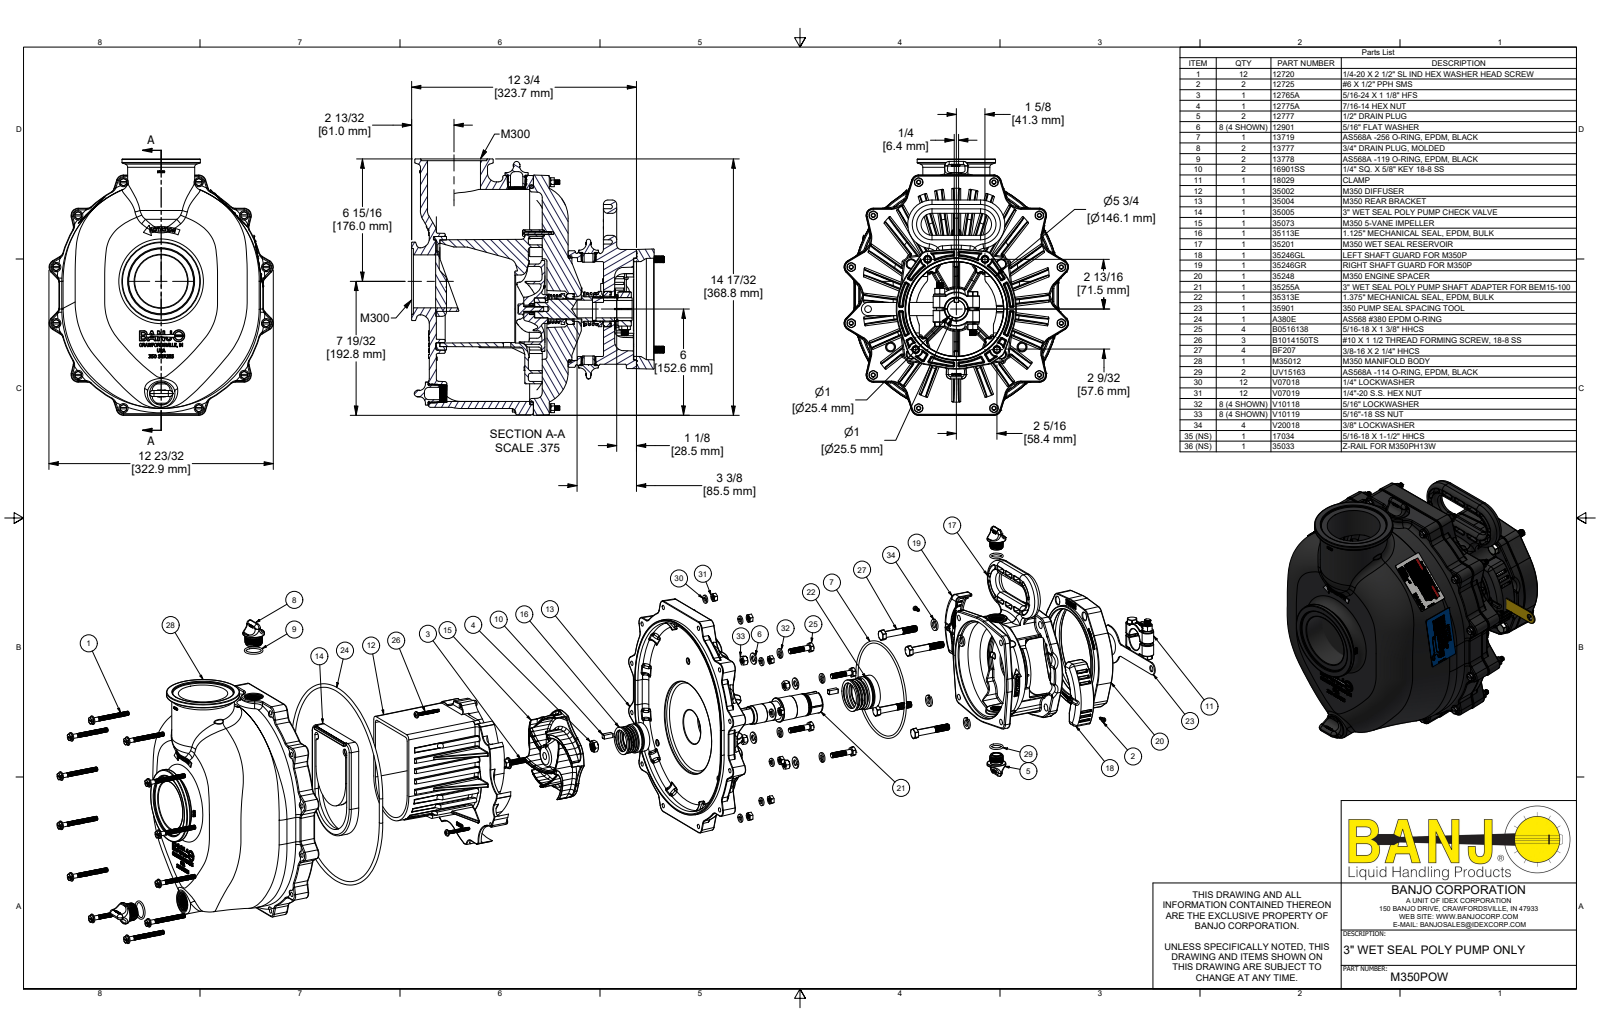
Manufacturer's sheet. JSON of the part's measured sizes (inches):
{"part_name": "M350POW; 35073; 35002; M35012 (+8 more)", "step_written_by": "Autodesk Inventor 2022 (AUTOMOTIVE_DESIGN)", "units": "inches", "bodies": {"solids": 106, "faces": 24916, "planar": 8794, "cylindrical": 3728, "other": 12394}, "overall_size": [14.518, 14.325, 12.712], "volume_in3": 353.6, "surface_area_in2": 2504, "round_holes": [[0.196, 12], [0.252, 12], [0.27, 12], [0.52, 10], [0.385, 6], [0.437, 5], [0.252, 4], [0.313, 4], [0.322, 4], [0.344, 4], [0.344, 4], [0.125, 3]], "round_bosses_or_shafts": [[0.324, 60], [0.337, 46], [0.489, 12], [0.25, 12], [0.687, 6], [0.375, 6], [0.721, 4], [0.688, 4]], "partial_cylinders_radius": [[0.031, 401], [0.062, 212], [0.016, 75], [0.094, 69], [0.25, 59], [0.125, 52], [0.375, 49], [0.12, 26]], "face_to_face_distances": [0.4, 6.4, 0.5, 0.9, 5.014, 4.05, 0.2, 0.269, 6.669, 1.386], "hole_center_spacings": [6.005, 3.182, 9.407, 3.611, 5.107, 6.137, 6.236, 6.408]}
